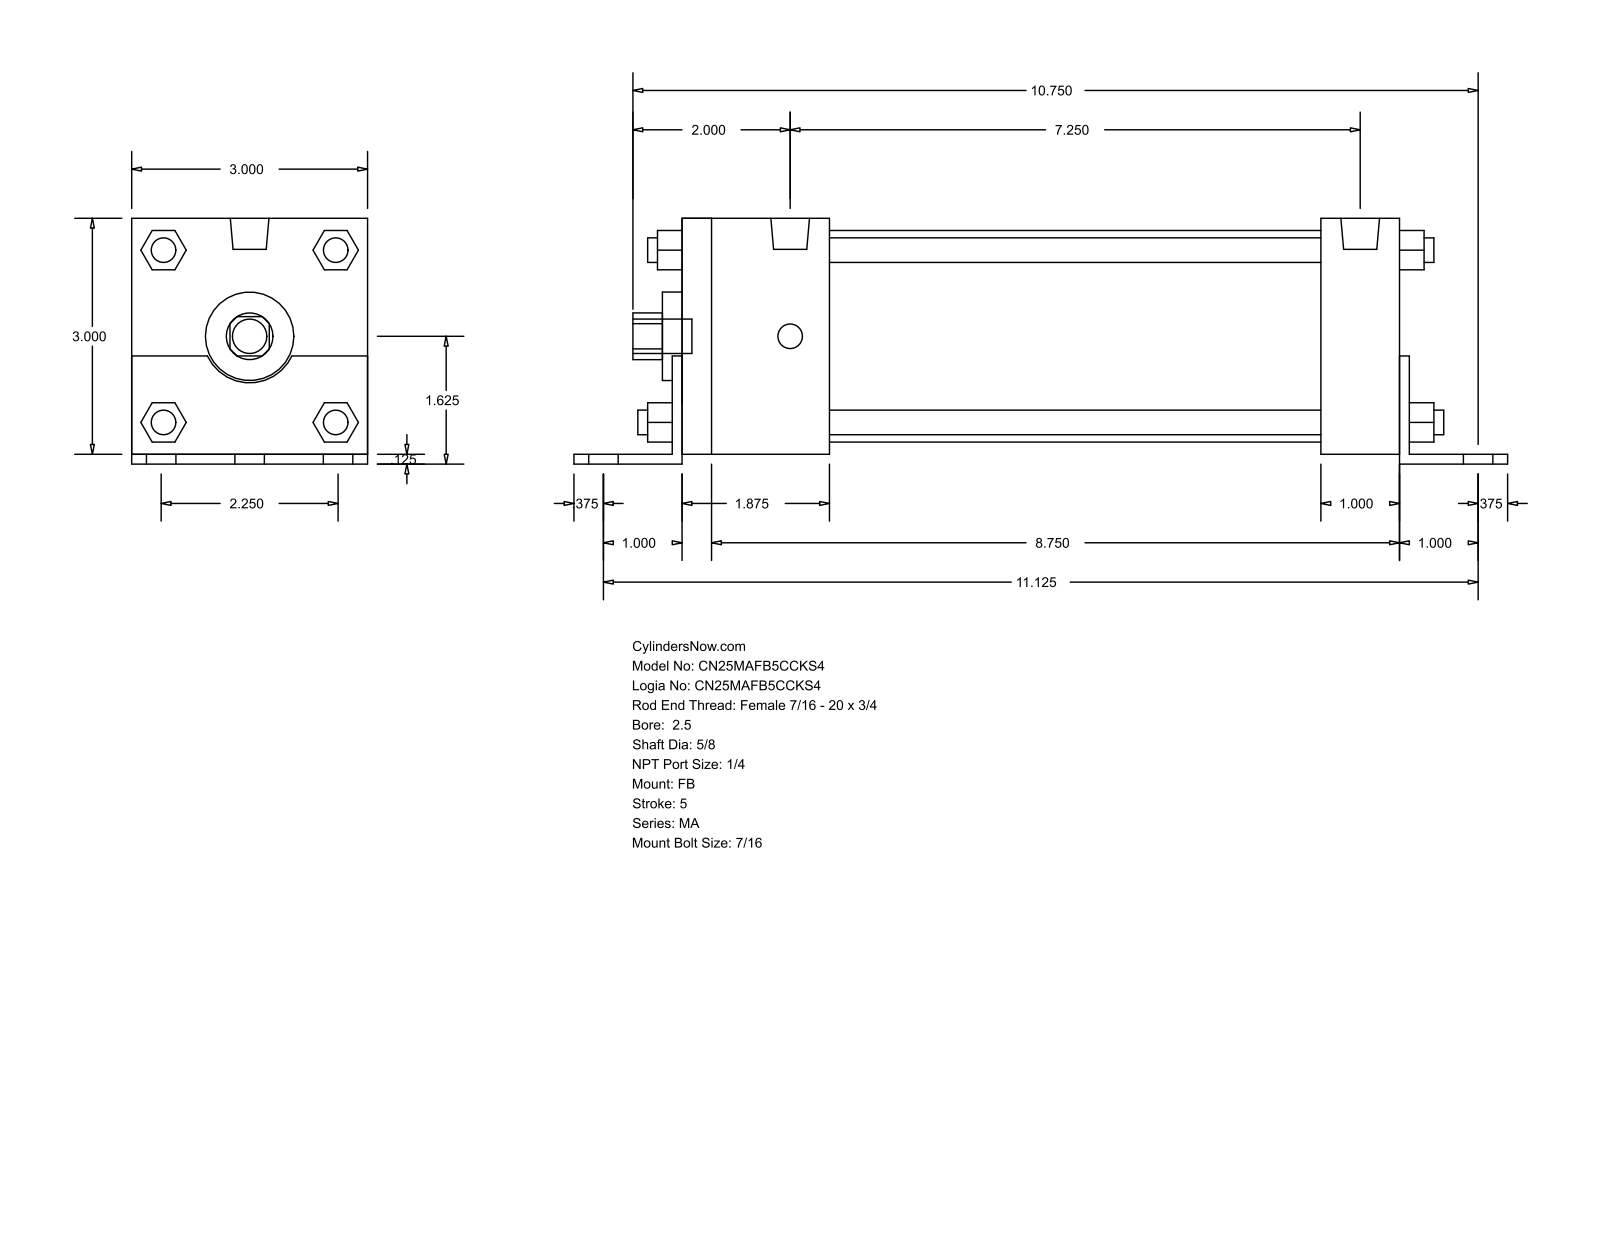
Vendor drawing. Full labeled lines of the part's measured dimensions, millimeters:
Part name (STEP PRODUCT): MA_FB__0250_0.625
STEP written by: GSSL Pune (CONFIG_CONTROL_DESIGN)
Units: millimetres
Bodies: 0 solids, 140 faces (105 planar, 35 cylindrical, 0 other)
Overall size (bounding box): 301.62 × 79.38 × 76.2
Round holes (diameter × count): ⌀15.88 ×1, ⌀28.57 ×1, ⌀68.33 ×1
Round bosses / shafts (diameter × count): ⌀7.94 ×8, ⌀11.11 ×7, ⌀12.49 ×2
Partial cylindrical surfaces — rounded edges, fillets, slot ends (radius × count): R7.54 ×1, R15.05 ×1
Main face-to-face distances: 76.2, 3.17, 79.37, 231.77, 238.12, 3.18, 234.94, 47.62, 25.4, 234.95
